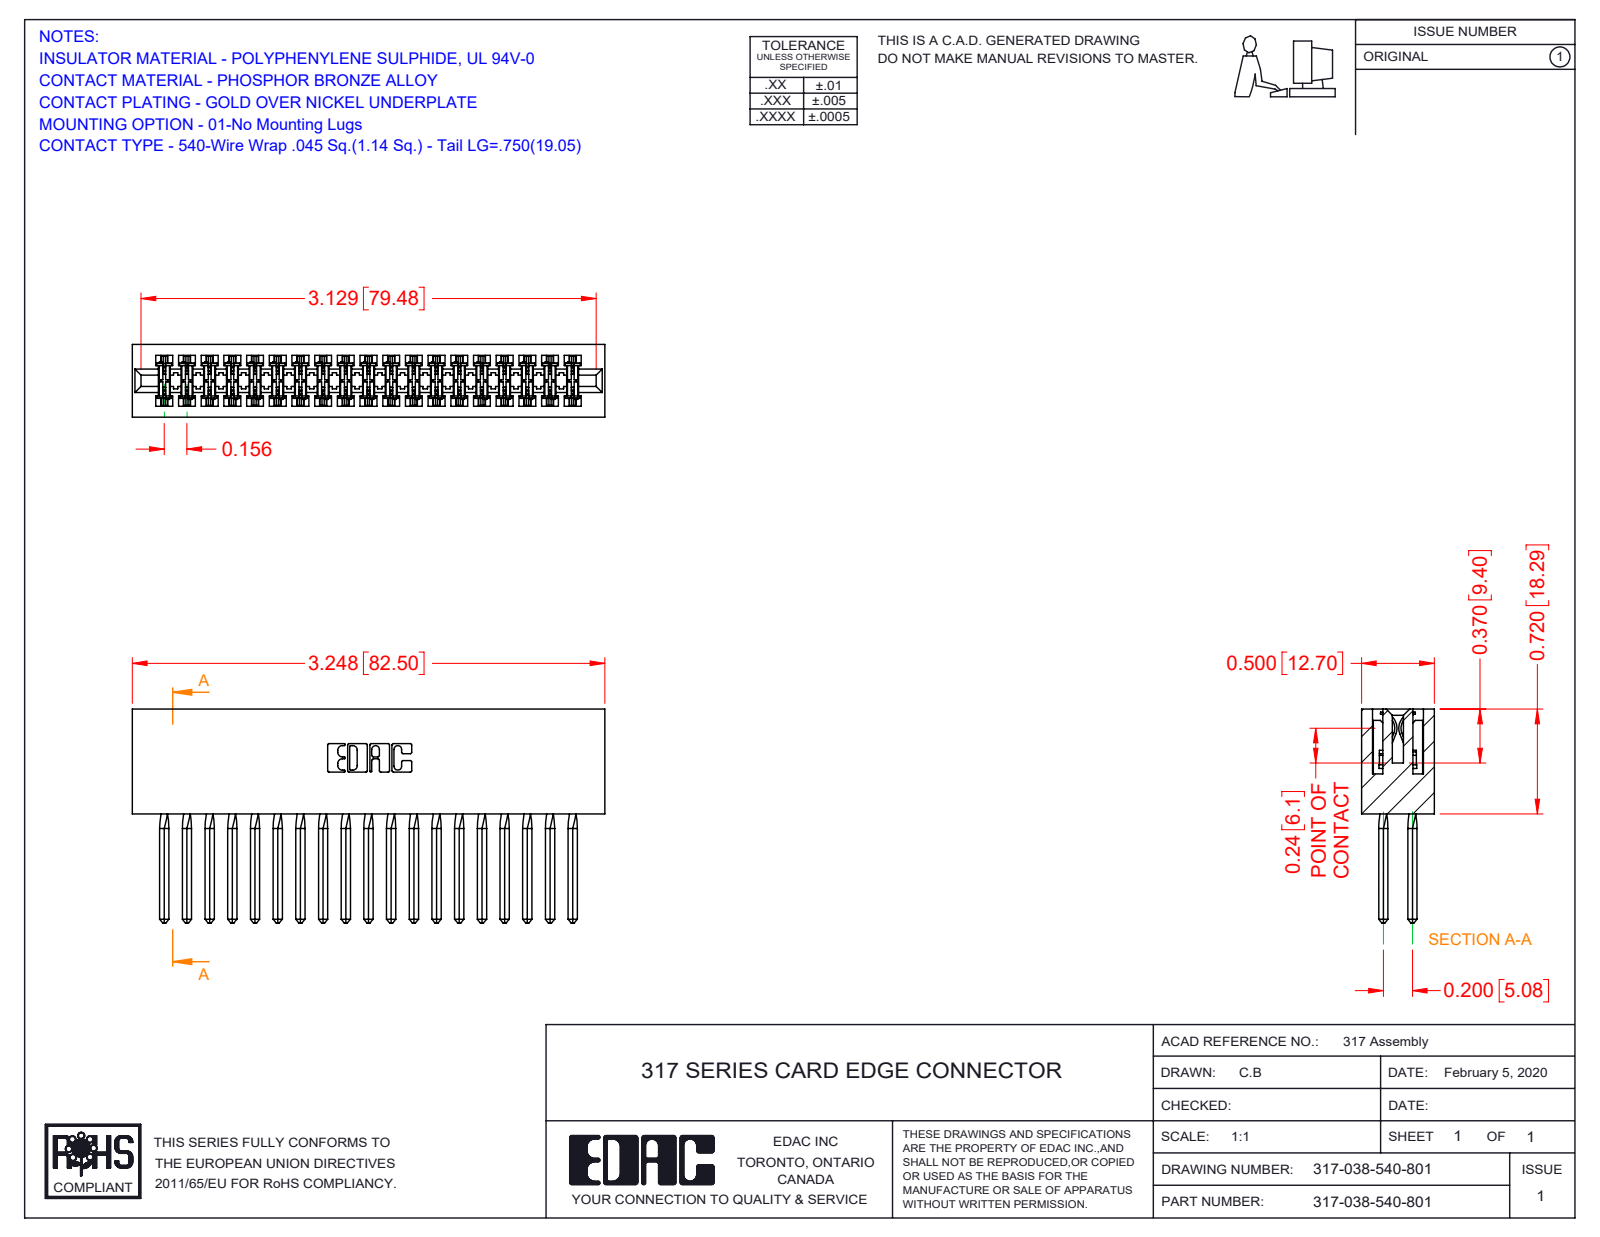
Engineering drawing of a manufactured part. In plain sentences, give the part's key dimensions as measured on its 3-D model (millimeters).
The part is named "317 Part_Lugless; 317-038-540-801; 317-290-001_540". Its 3-D file was written by "SolidWorks 2016 (CONFIG_CONTROL_DESIGN)". It is 39 solids with 3472 faces: 2824 planar, 496 cylindrical and 152 other. Overall it measures 82.5 by 37.3 by 12.7 millimeters. Its volume is 14 900 cubic millimeters and its surface area 21 550 square millimeters. Partial cylindrical surfaces (rounded edges, fillets, slot ends): 76 of radius 0.4, 22 of radius 0.3, 6 of radius 0.2, 6 of radius 0.8, 3 of radius 0.7, 2 of radius 2.4, 2 of radius 2.5, 2 of radius 2.8. The main face-to-face distances are 12.7, 1.9, 10.8, 2.8, 8.9, 5, 5.6, 18.3, 2.9, 2.4.
